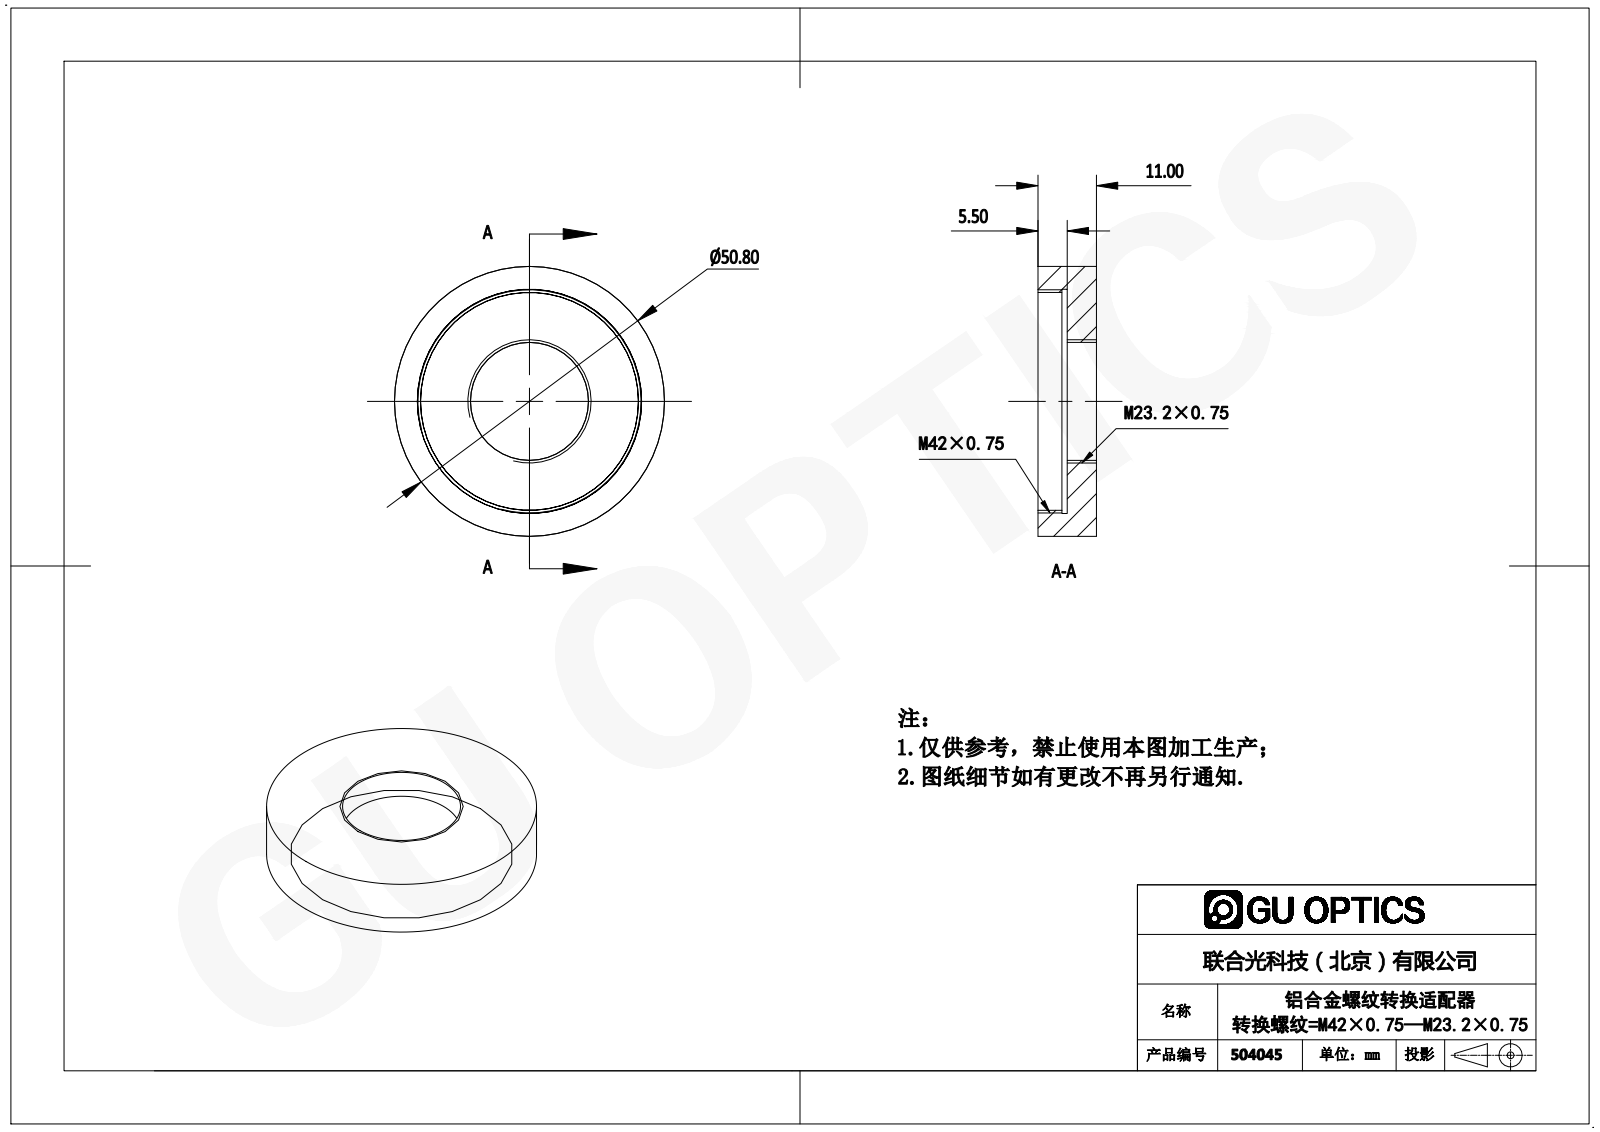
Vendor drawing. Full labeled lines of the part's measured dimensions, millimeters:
Part name (STEP PRODUCT): 504045
STEP written by: SolidWorks 2016 (AUTOMOTIVE_DESIGN)
Units: millimetres
Bodies: 1 solid, 12 faces (4 planar, 8 cylindrical, 0 other)
Overall size (bounding box): 50.8 × 50.8 × 11
Volume: 12 826 mm³ · Surface area: 6 288 mm²
Round holes (diameter × count): ⌀22.2 ×1, ⌀41 ×1, ⌀42.2 ×1
Round bosses / shafts (diameter × count): ⌀50.8 ×1
Main face-to-face distances: 5.5, 11, 4.5, 1, 6.5
